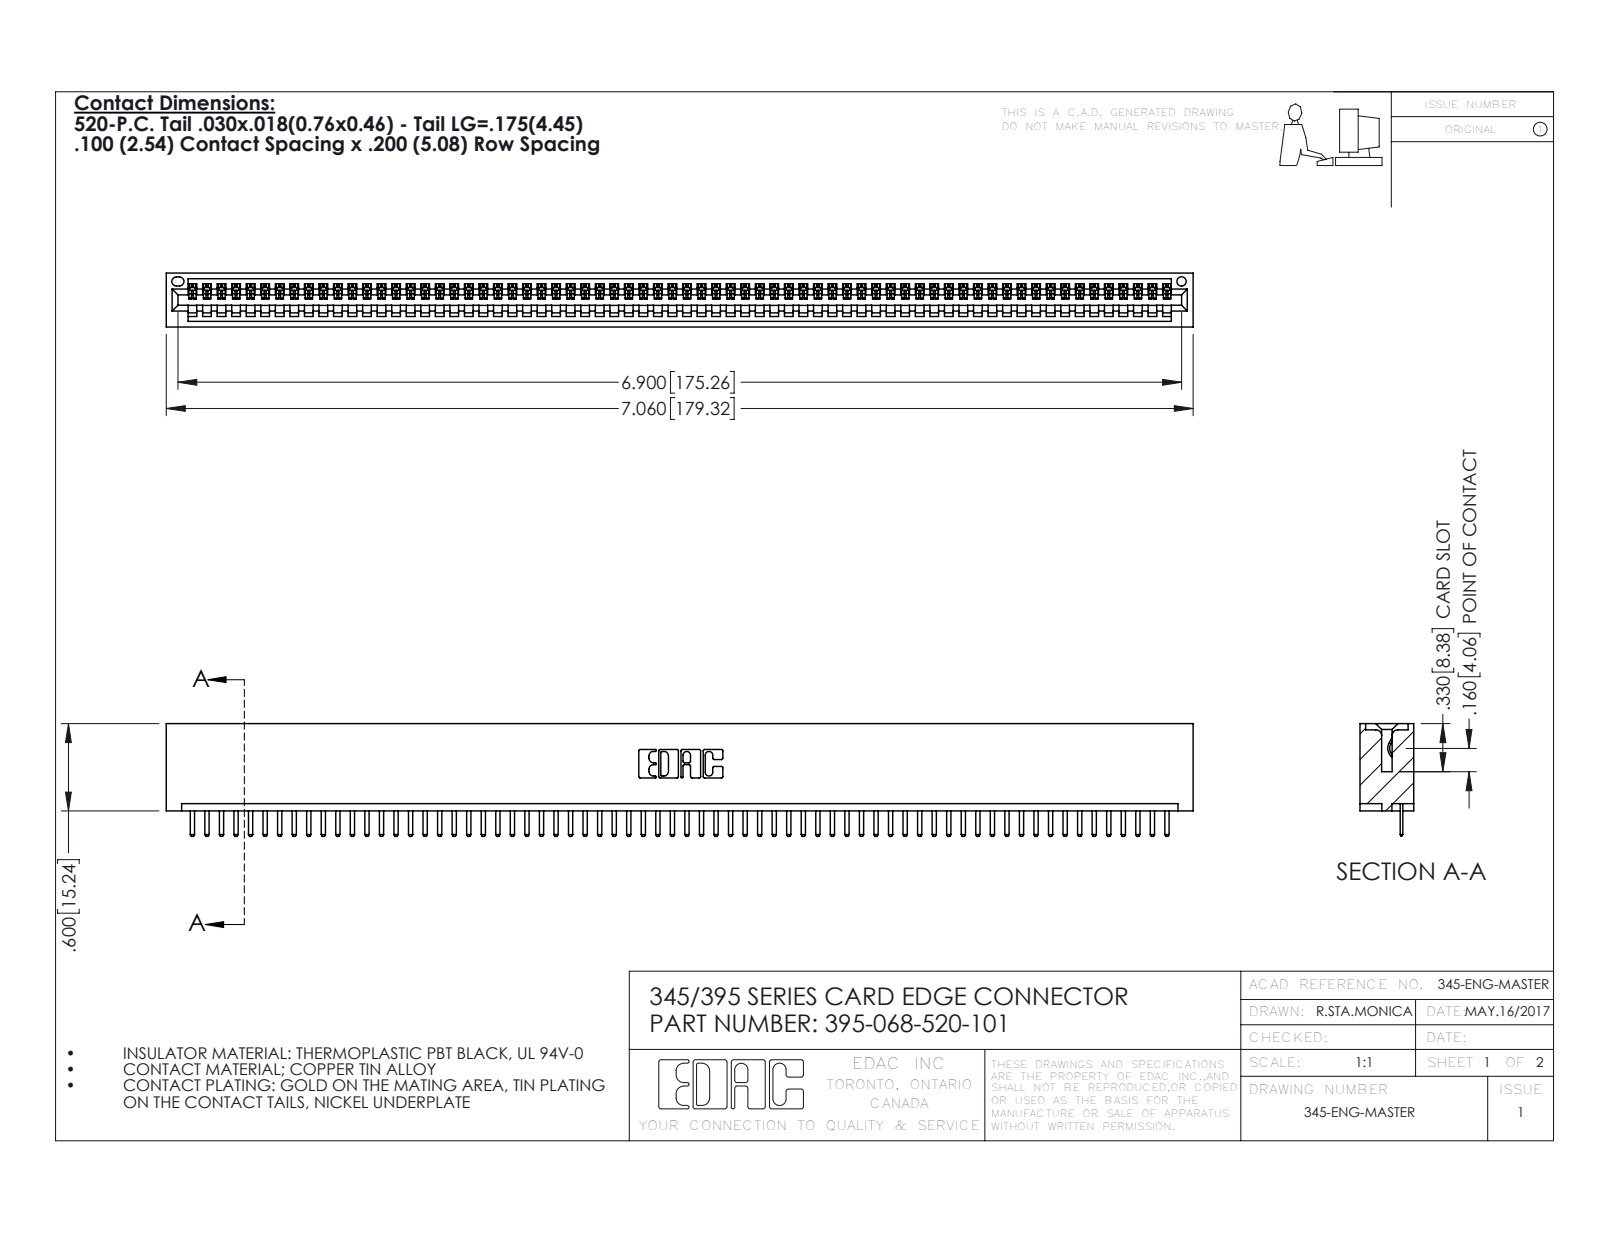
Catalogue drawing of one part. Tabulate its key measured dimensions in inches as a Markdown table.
| quantity | value |
| --- | --- |
| part name | 345 Part_No Mounting Lugs; 395-068-520-101; 345-292-001_345-293-120 |
| STEP written by | SolidWorks 2016 (CONFIG_CONTROL_DESIGN) |
| units | inches |
| bodies | 69 solids, 4334 faces (2932 planar, 1402 cylindrical, 0 other) |
| overall size | 7.06 × 0.775 × 0.37 |
| volume | 1.076 in³ |
| surface area | 36.17 in² |
| round holes (diameter × count) | 0.064 × 1 |
| partial cylindrical surfaces (radius × count) | 0.01 × 138, 0.006 × 136, 0.01 × 22, 0.007 × 6, 0.031 × 6, 0.026 × 3, 0.031 × 2, 0.04 × 2 |
| main face-to-face distances | 0.298, 0.072, 0.37, 0.2, 0.098, 0.272, 0.025, 0.225, 0.072, 0.149 |
